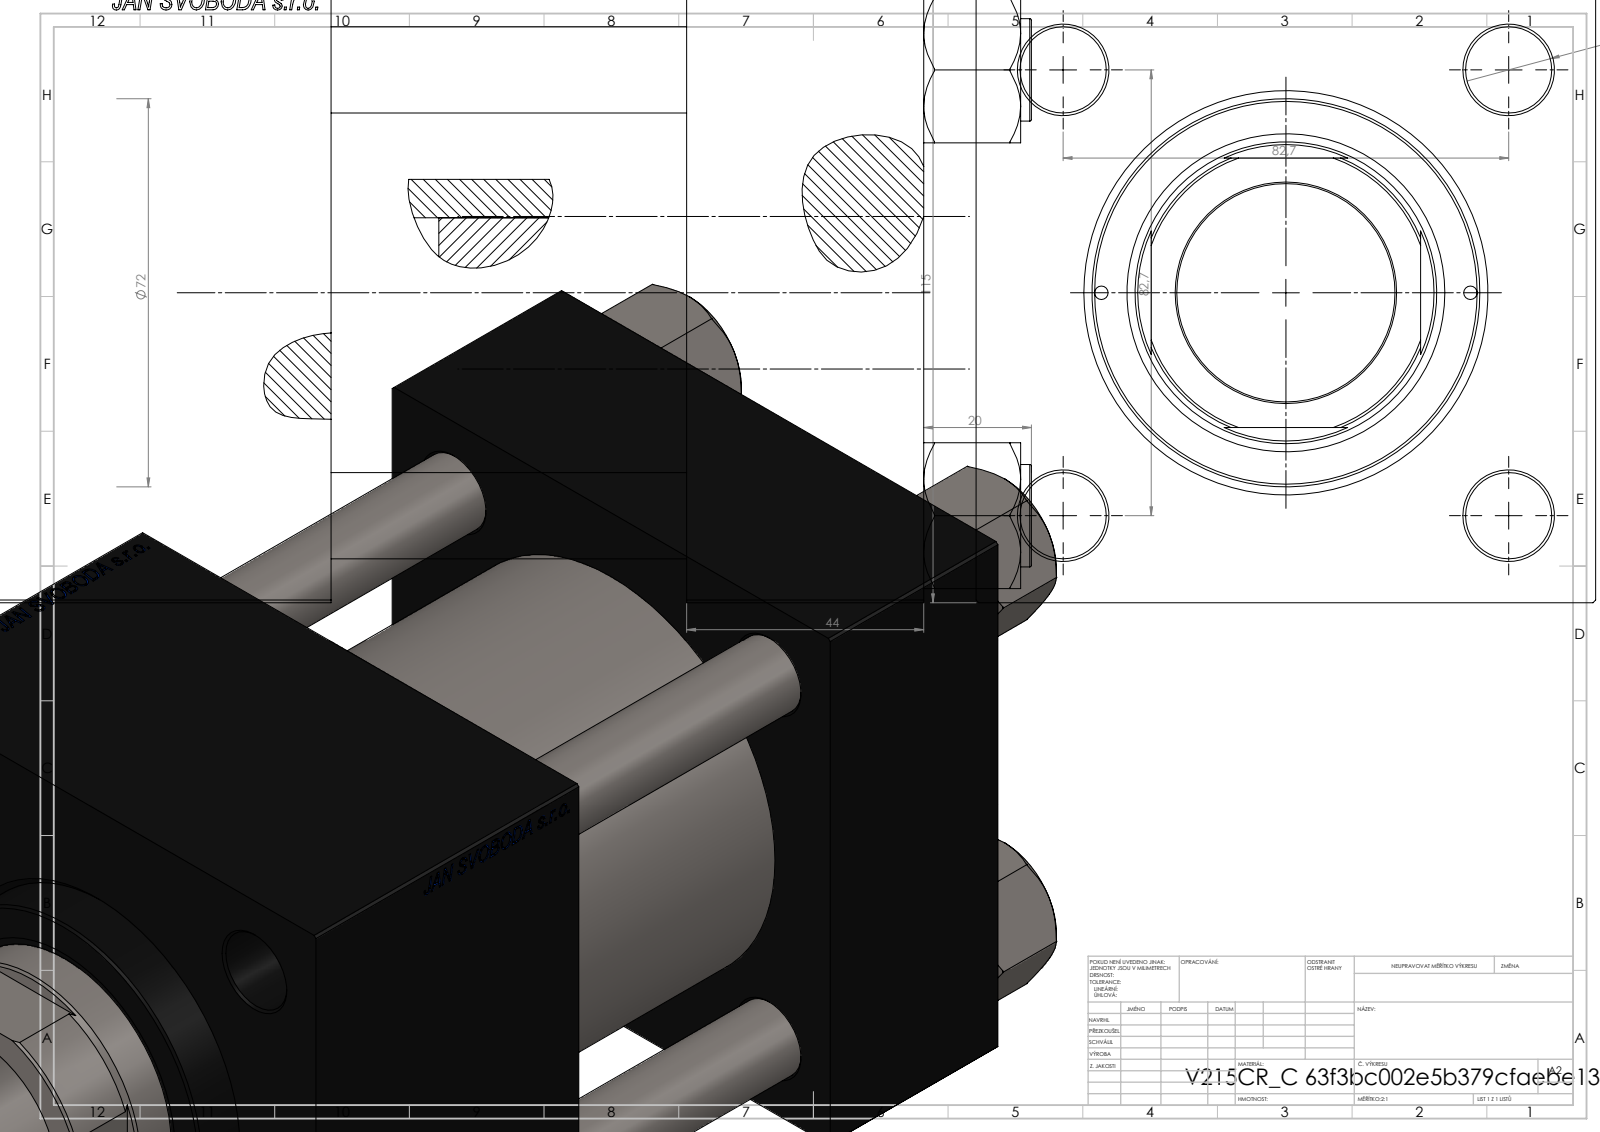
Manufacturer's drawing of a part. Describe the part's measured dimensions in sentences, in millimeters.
The part is named "V215CR_C_Body; NUT_M5_C; V215CR_C_TYCINKA; V215CR_VCP_C (+1 more)". Its 3-D file was written by "SolidWorks 2019 (CONFIG_CONTROL_DESIGN)". It is 11 solids with 1199 faces: 575 planar, 88 cylindrical and 536 other. Overall it measures 230 by 115 by 115 millimeters. Its volume is 1 862 000 cubic millimeters and its surface area 280 435 square millimeters. Round holes: 4 of diameter 16, 2 of diameter 2.5, 2 of diameter 7, 2 of diameter 26.44, 2 of diameter 35, 1 of diameter 40.5, 1 of diameter 56, 1 of diameter 59, 1 of diameter 61, 1 of diameter 72, 1 of diameter 80. Round bosses or shafts: 4 of diameter 19, 1 of diameter 86. Partial cylindrical surfaces (rounded edges, fillets, slot ends): 1 of radius 27. The main face-to-face distances are 115, 44, 110, 66, 179, 135, 69, 20, 150.3, 106.3. The hole center spacings are 41.96, 58.48, 82.7, 86.17, 34.25, 116.96, 68.5, 111.
